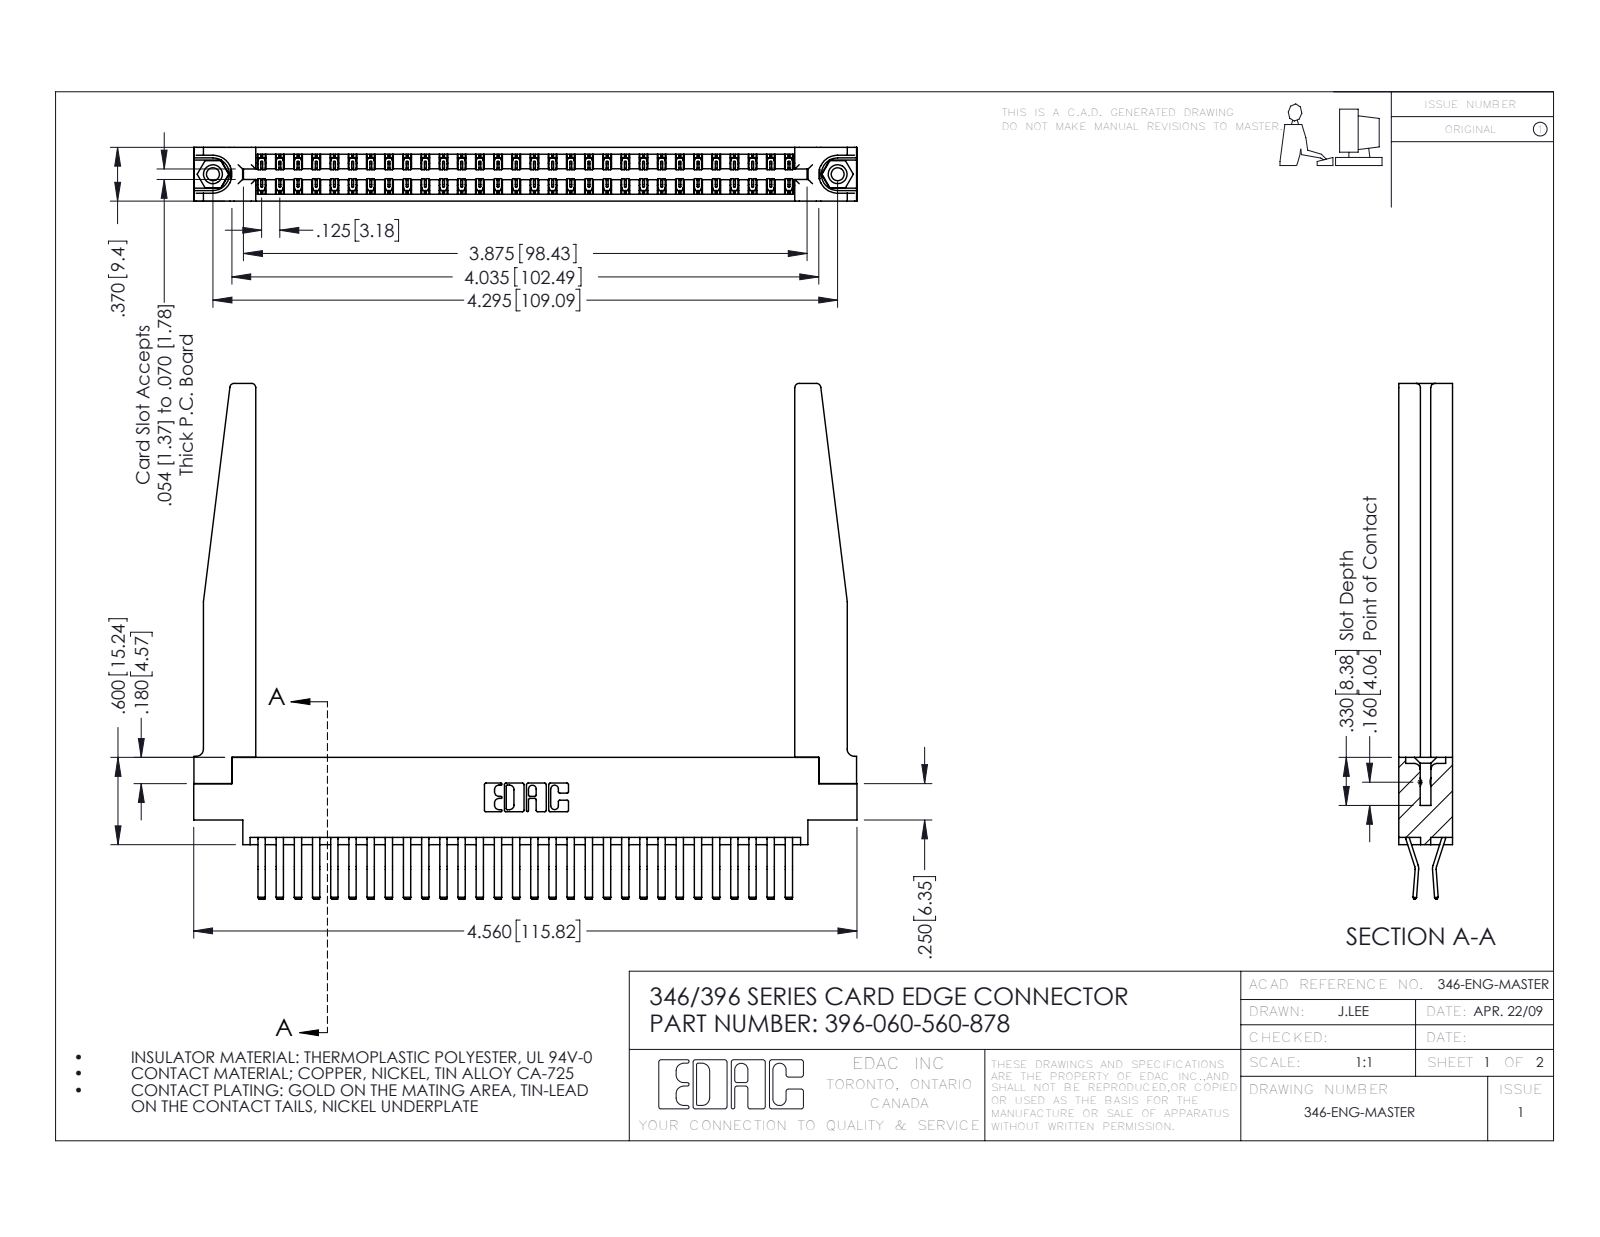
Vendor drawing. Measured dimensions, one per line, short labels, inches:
name: 346 Part_0.170 Offset - 0.156 Dia-TH; 345-292-001_560 Tail; 346-220-078_345-220-078; 396-060-560-878 (+1 more)
written by: SolidWorks 2016 (CONFIG_CONTROL_DESIGN)
unit: in
bodies: 65 solids, 3600 faces (2322 planar, 1226 cylindrical, 52 other)
size: 4.56 × 3.545 × 0.37
volume: 1.12 in³; area: 36.12 in²
holes: 2× ⌀0.089, 2× ⌀0.125, 2× ⌀0.156, 1× ⌀0.064
bosses: 2× ⌀0.155
rounds: 90× R0.006, 22× R0.01, 8× R0.03, 6× R0.007, 6× R0.031, 4× R0.05, 3× R0.026, 2× R0.01
face distances: 0.37, 0.048, 0.322, 0.072, 0.148, 0.15, 0.025, 0.25, 0.298, 0.275
hole spacings: 0.246, 4.087, 4.295
